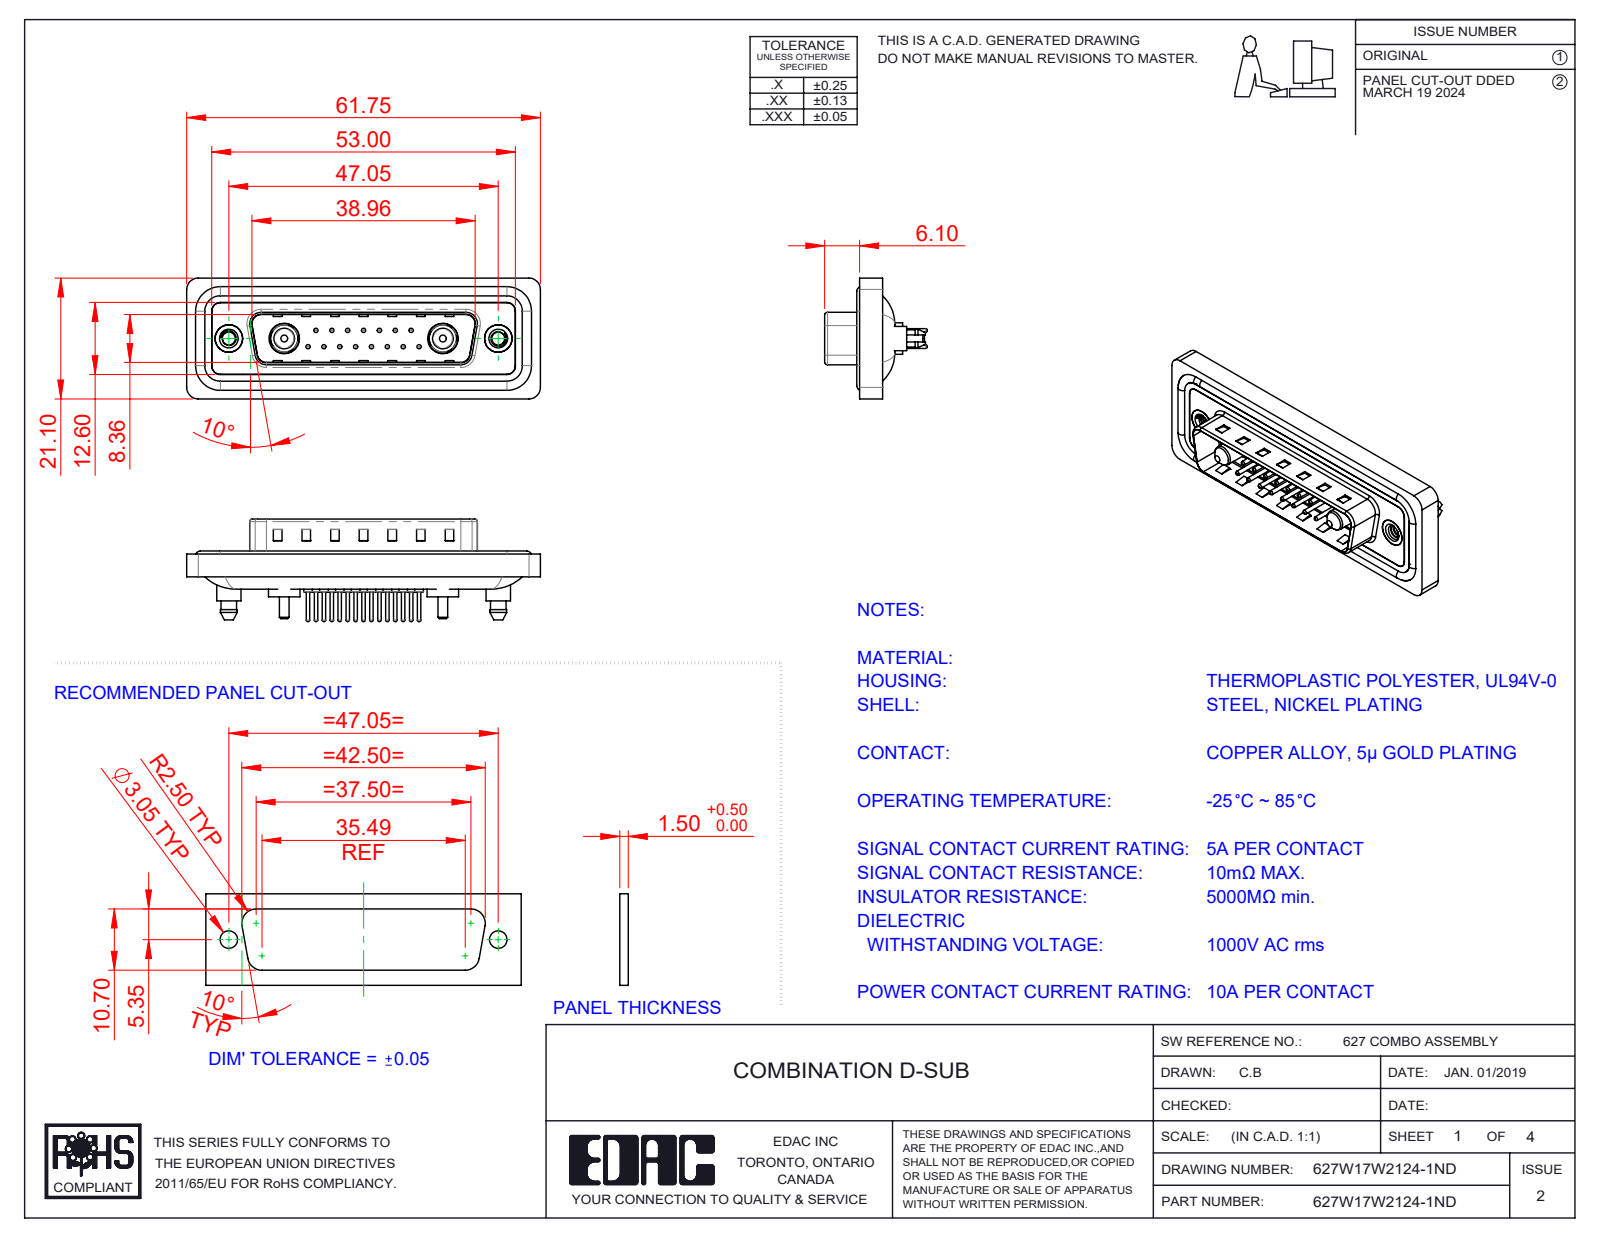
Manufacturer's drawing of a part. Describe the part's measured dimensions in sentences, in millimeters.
The part is named "627Combo Threaded Boardlock_5; 627Combo Housing_17W2; 627Combo Shell Rear_25 Contacts; 627Combo Contact Row 2_24 (+6 more)". Its 3-D file was written by "SolidWorks 2023 (CONFIG_CONTROL_DESIGN)". It is 26 solids with 1174 faces: 350 planar, 476 cylindrical and 348 other. Overall it measures 61.75 by 21.1 by 17.9 millimeters. Its volume is 7 372 cubic millimeters and its surface area 12 225 square millimeters. Round holes: 15 of diameter 0.75, 15 of diameter 1.6, 15 of diameter 2, 2 of diameter 2.26, 2 of diameter 4, 2 of diameter 4.8, 2 of diameter 4.85, 2 of diameter 5, 2 of diameter 5.3. Round bosses or shafts: 15 of diameter 1.5, 15 of diameter 0.6, 4 of diameter 1.6, 2 of diameter 5.5, 2 of diameter 5.4, 2 of diameter 5.2, 2 of diameter 4.9, 2 of diameter 4.75. Partial cylindrical surfaces (rounded edges, fillets, slot ends): 24 of radius 1.5, 18 of radius 2, 10 of radius 1.6, 8 of radius 0.5, 4 of radius 0.25, 4 of radius 0.6, 4 of radius 0.65, 4 of radius 0.9. The main face-to-face distances are 0.4, 1.5, 1.1, 1.6, 0.5, 3.1, 2.9, 0.82, 9.58, 4.1. The hole center spacings are 3.16, 2.77, 5.54, 8.31, 5.04, 7.49, 11.08, 5.03.
